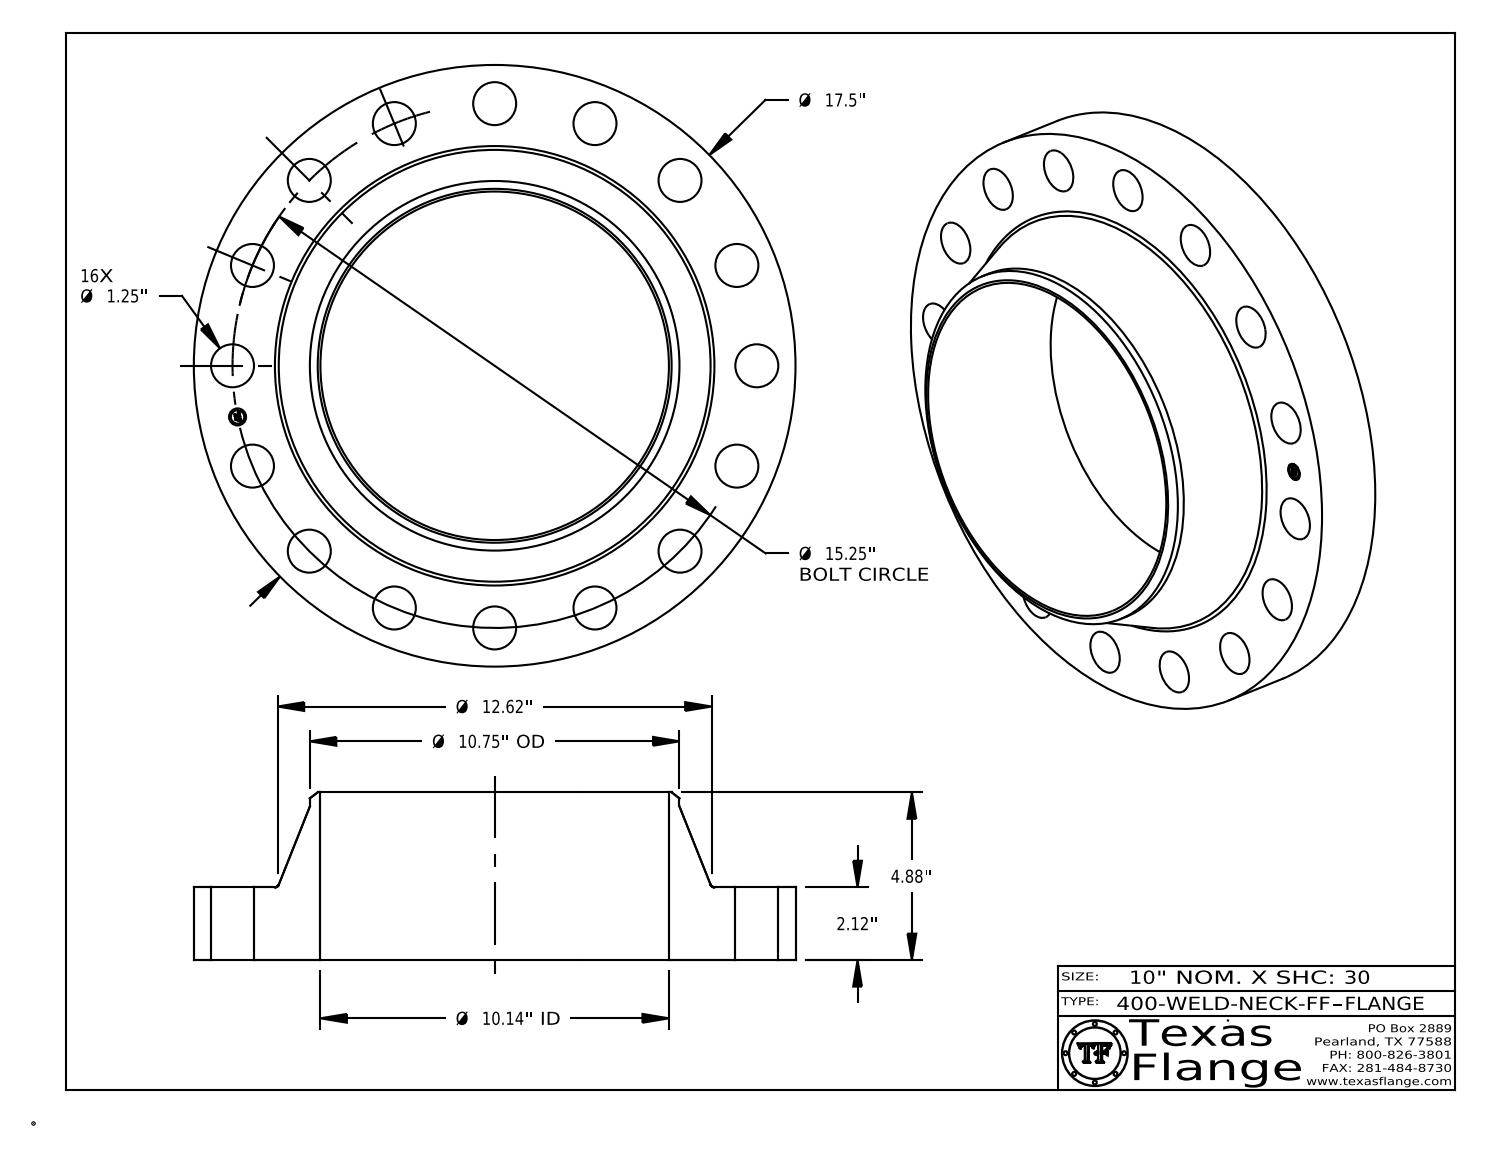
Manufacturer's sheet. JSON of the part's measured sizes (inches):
{"part_name": "400-WELD-NECK-FF", "step_written_by": "CATIA V5 STEP AP214 (AUTOMOTIVE_DESIGN)", "units": "inches", "bodies": {"solids": 1, "faces": 432, "planar": 368, "cylindrical": 58, "other": 6}, "overall_size": [17.5, 17.5, 4.88], "volume_in3": 363.6, "surface_area_in2": 753.3, "round_holes": [[1.25, 16], [0.495, 1], [10.136, 1]], "round_bosses_or_shafts": [[0.03, 8], [17.5, 1], [10.75, 1], [0.39, 1]], "face_to_face_distances": [2.12, 4.88, 2.76, 0.015, 2.105, 2.775, 0.148, 0.145, 0.027, 0.096], "hole_center_spacings": [8.472, 10.783, 14.957, 14.089, 7.625, 2.975, 2.975, 5.836]}
